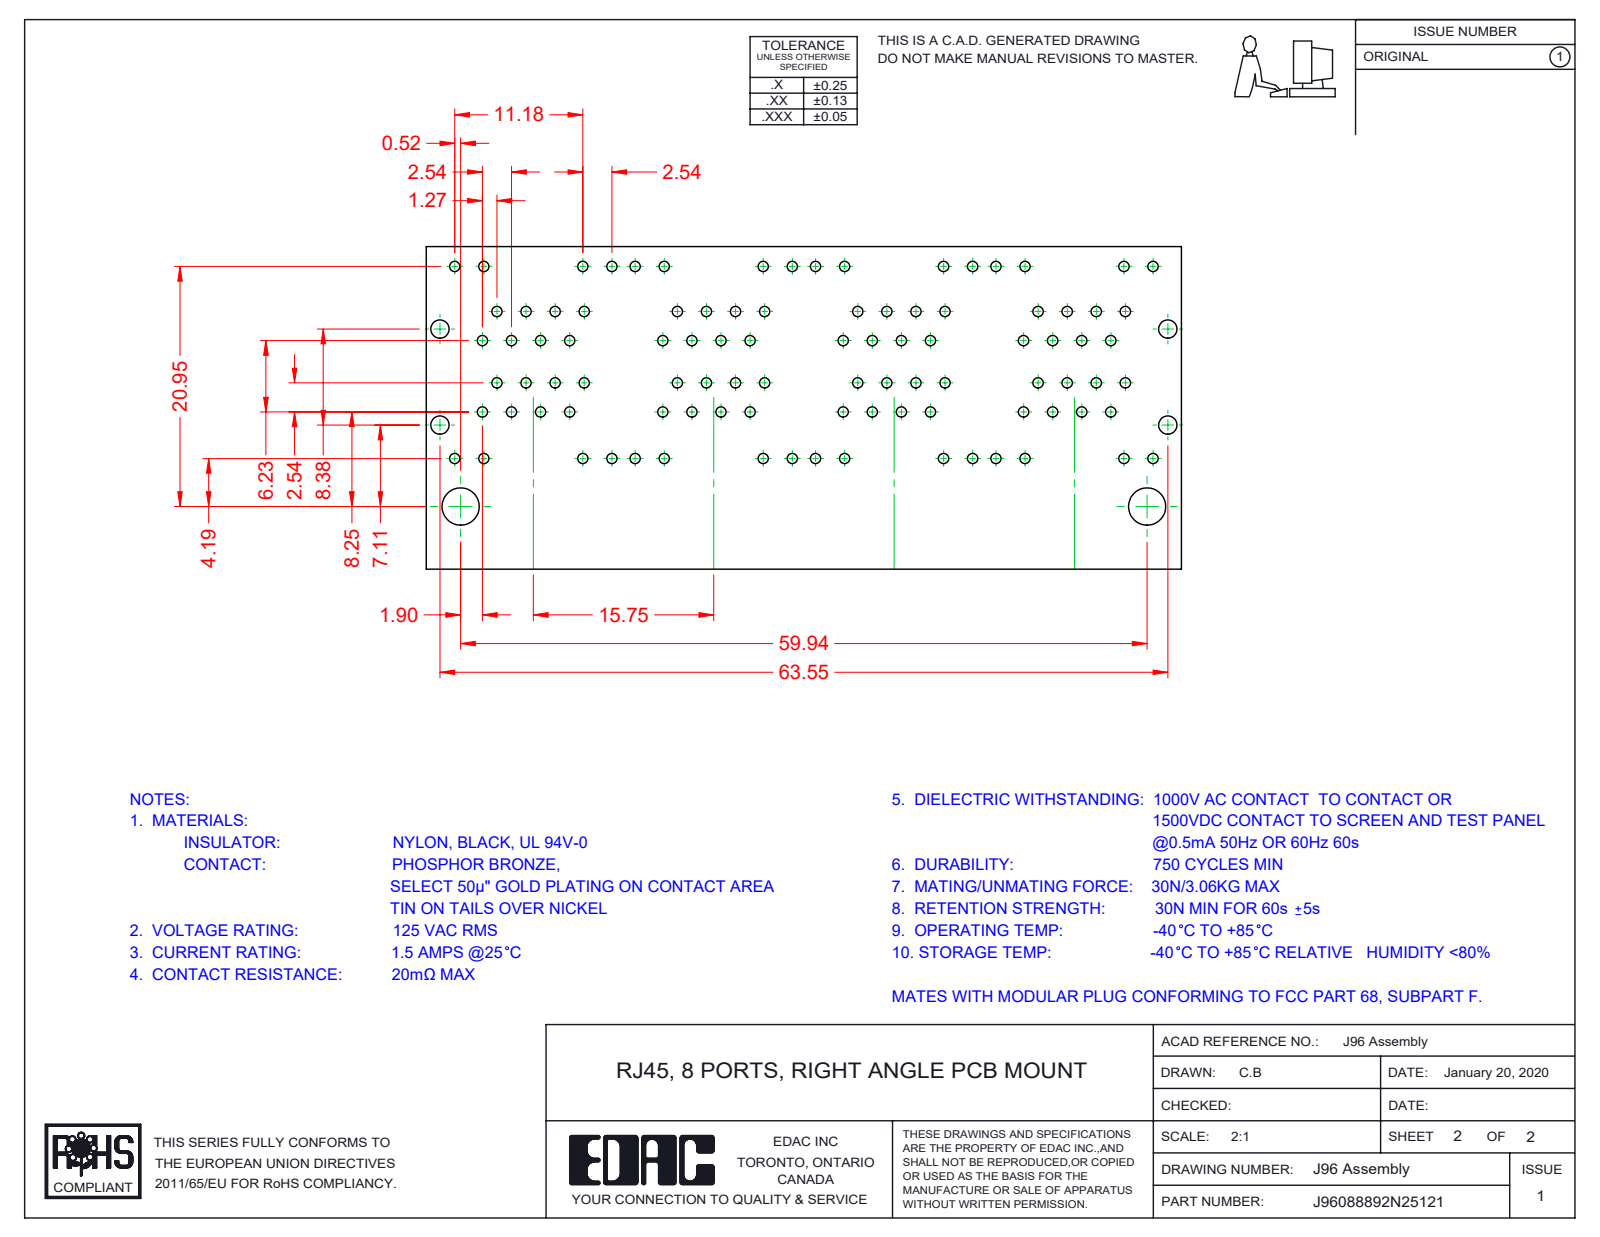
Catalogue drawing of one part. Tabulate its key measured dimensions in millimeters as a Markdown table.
| quantity | value |
| --- | --- |
| part name | 96 Insulator Insert; 96 LED LH Lower_2-Red; 96 Contacts Upper; 96 Back Plate_8 Ports (+8 more) |
| STEP written by | SolidWorks 2016 (CONFIG_CONTROL_DESIGN) |
| units | millimeters |
| bodies | 96 solids, 7658 faces (6069 planar, 1323 cylindrical, 266 other) |
| overall size | 64.05 × 29.58 × 28.68 |
| volume | 24 160 mm³ |
| surface area | 63 658 mm² |
| round holes (diameter × count) | 1.7 × 3 |
| round bosses / shafts (diameter × count) | 1.68 × 3 |
| partial cylindrical surfaces (radius × count) | 0.25 × 124, 0.35 × 73, 1 × 72, 0.5 × 49, 0.91 × 32, 0.2 × 21, 0.7 × 11, 0.22 × 8 |
| main face-to-face distances | 15.75, 0.35, 9.95, 1.17, 1.6, 0.54, 9.98, 10.18, 12.67, 3.37 |
| hole center spacings | 15.75, 31.5 |
